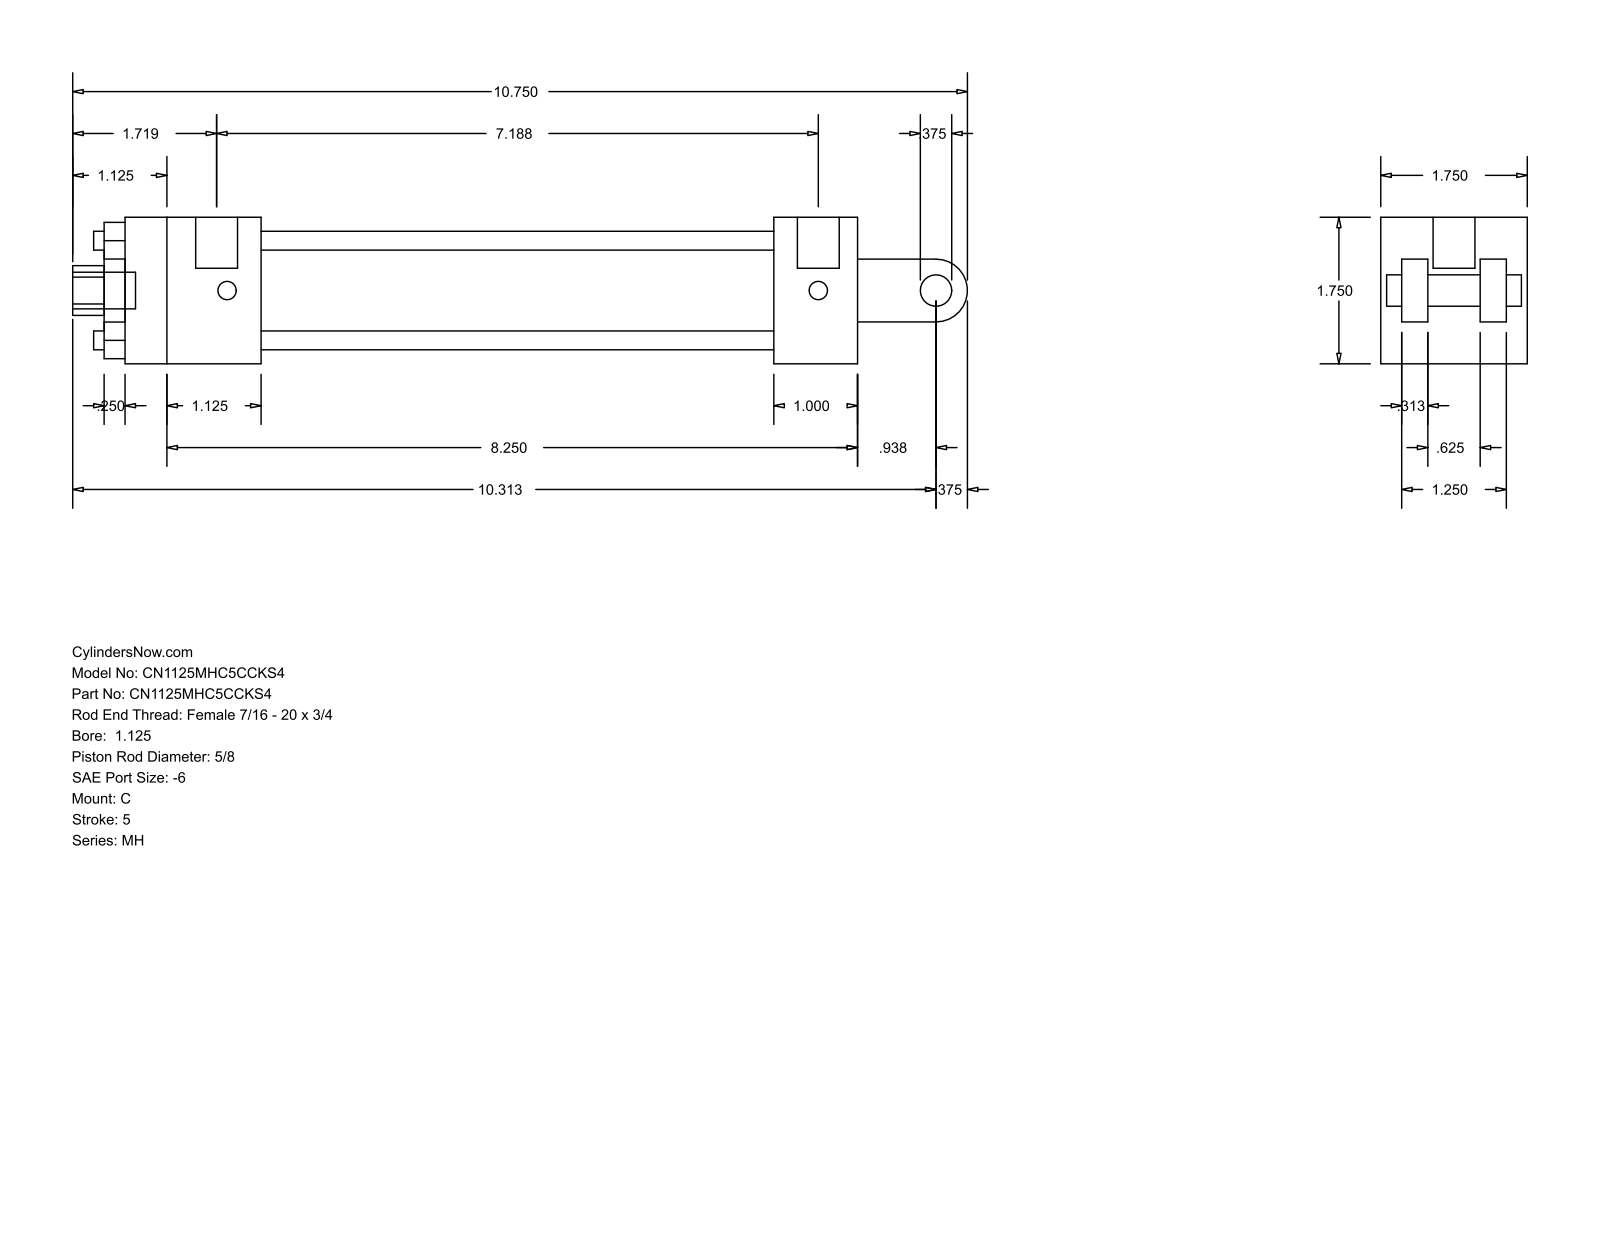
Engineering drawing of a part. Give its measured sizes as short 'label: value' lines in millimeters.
name: MH_C__0112_0.625
written by: GSSL Pune (CONFIG_CONTROL_DESIGN)
unit: mm
bodies: 0 solids, 99 faces (70 planar, 29 cylindrical, 0 other)
size: 271.46 × 44.45 × 44.45
holes: 4× ⌀5.71, 2× ⌀5.56, 1× ⌀12.7, 1× ⌀15.88, 1× ⌀28.57, 1× ⌀34.92
bosses: 2× ⌀5.56, 1× ⌀12.7, 1× ⌀11.11, 1× ⌀9.53
rounds: 1× R7.54, 1× R9.53
face distances: 44.46, 6.35, 31.76, 14.29, 12.7, 30.17, 38.11, 7.94, 23.82, 25.4
hole spacings: 21.37, 30.22, 42.74
